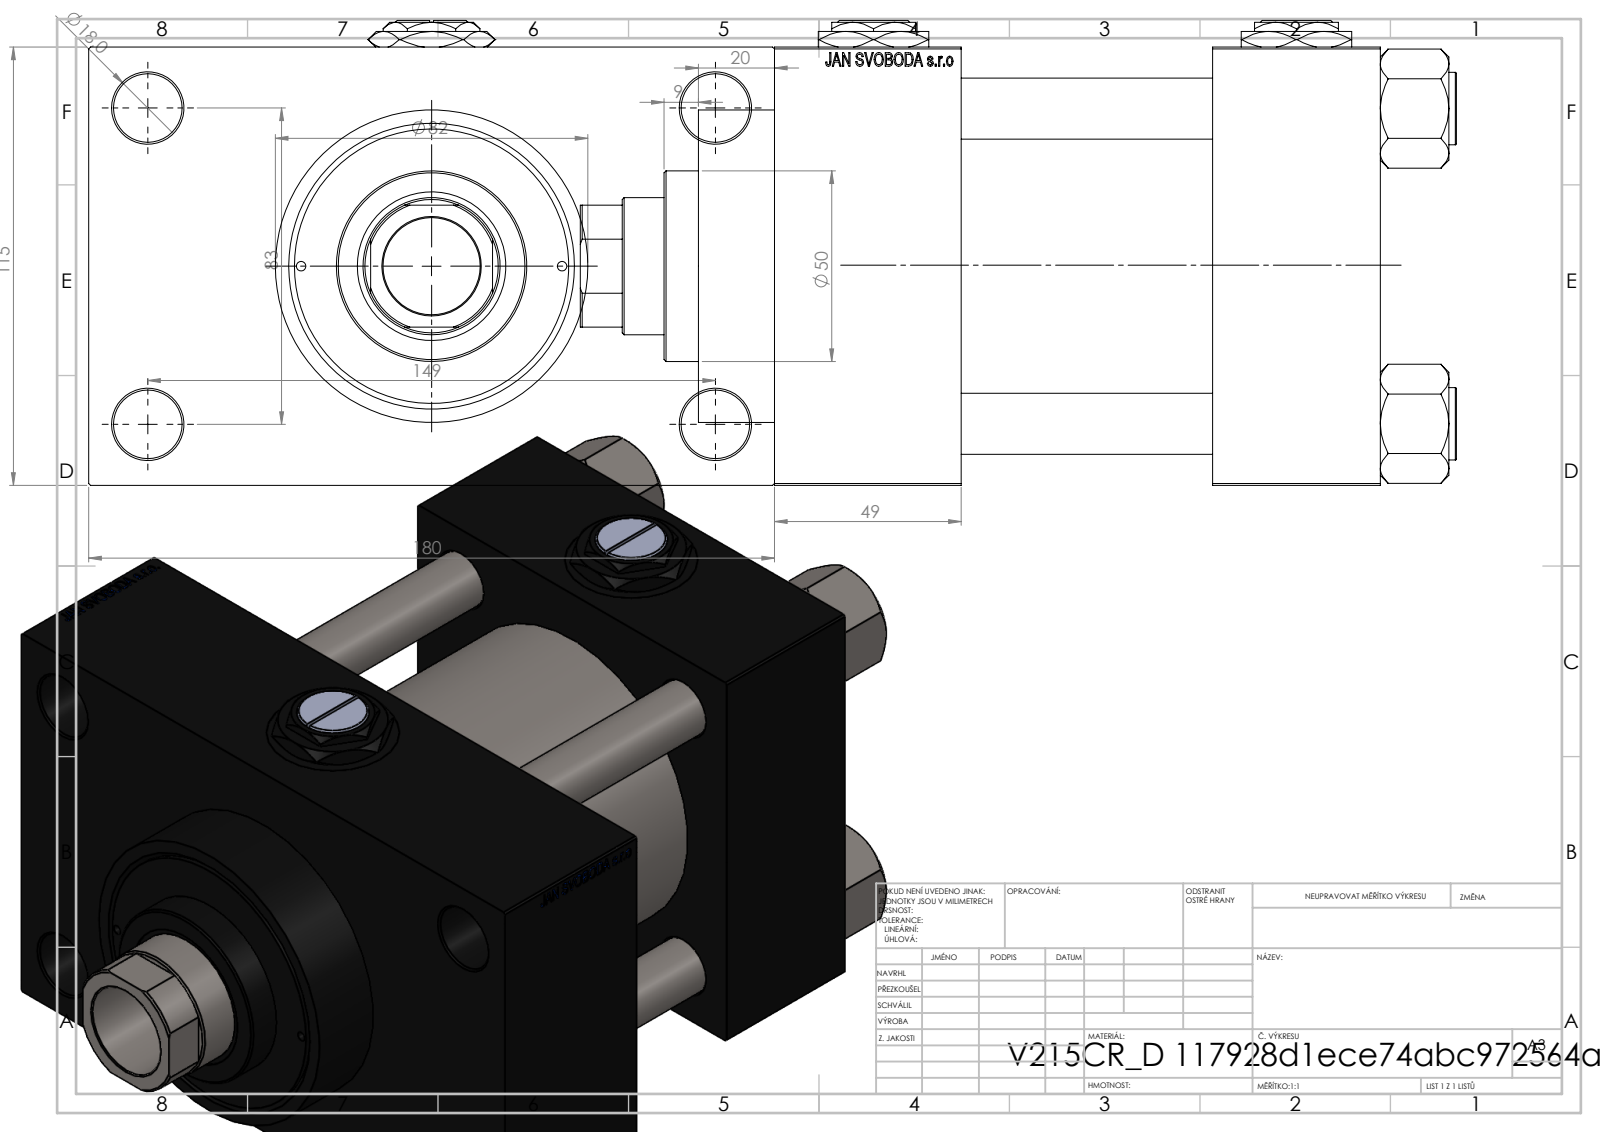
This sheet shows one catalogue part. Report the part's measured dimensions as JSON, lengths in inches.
{"part_name": "Zatka_pro_OIL_PORT; V215CR_VCP_D; V215CR_D_TYCINKA; V215_VC_A (+2 more)", "step_written_by": "SolidWorks 2019 (CONFIG_CONTROL_DESIGN)", "units": "inches", "bodies": {"solids": 13, "faces": 1260, "planar": 595, "cylindrical": 103, "other": 562}, "overall_size": [9.055, 7.087, 4.803], "volume_in3": 119.9, "surface_area_in2": 469.9, "round_holes": [[0.63, 4], [0.709, 4], [1.041, 4], [1.378, 4], [0.276, 3], [0.098, 2], [1.004, 1], [1.417, 1], [1.535, 1], [2.402, 1], [2.835, 1], [3.15, 1]], "round_bosses_or_shafts": [[0.748, 4], [3.386, 1], [3.228, 1], [1.969, 1]], "partial_cylinders_radius": [[0.689, 1]], "face_to_face_distances": [4.528, 2.598, 4.331, 1.929, 1.732, 6.26, 1.28, 5.807, 0.787, 2.717], "hole_center_spacings": [1.305, 1.652, 2.276, 2.302, 3.256, 3.357, 3.393, 3.513]}
